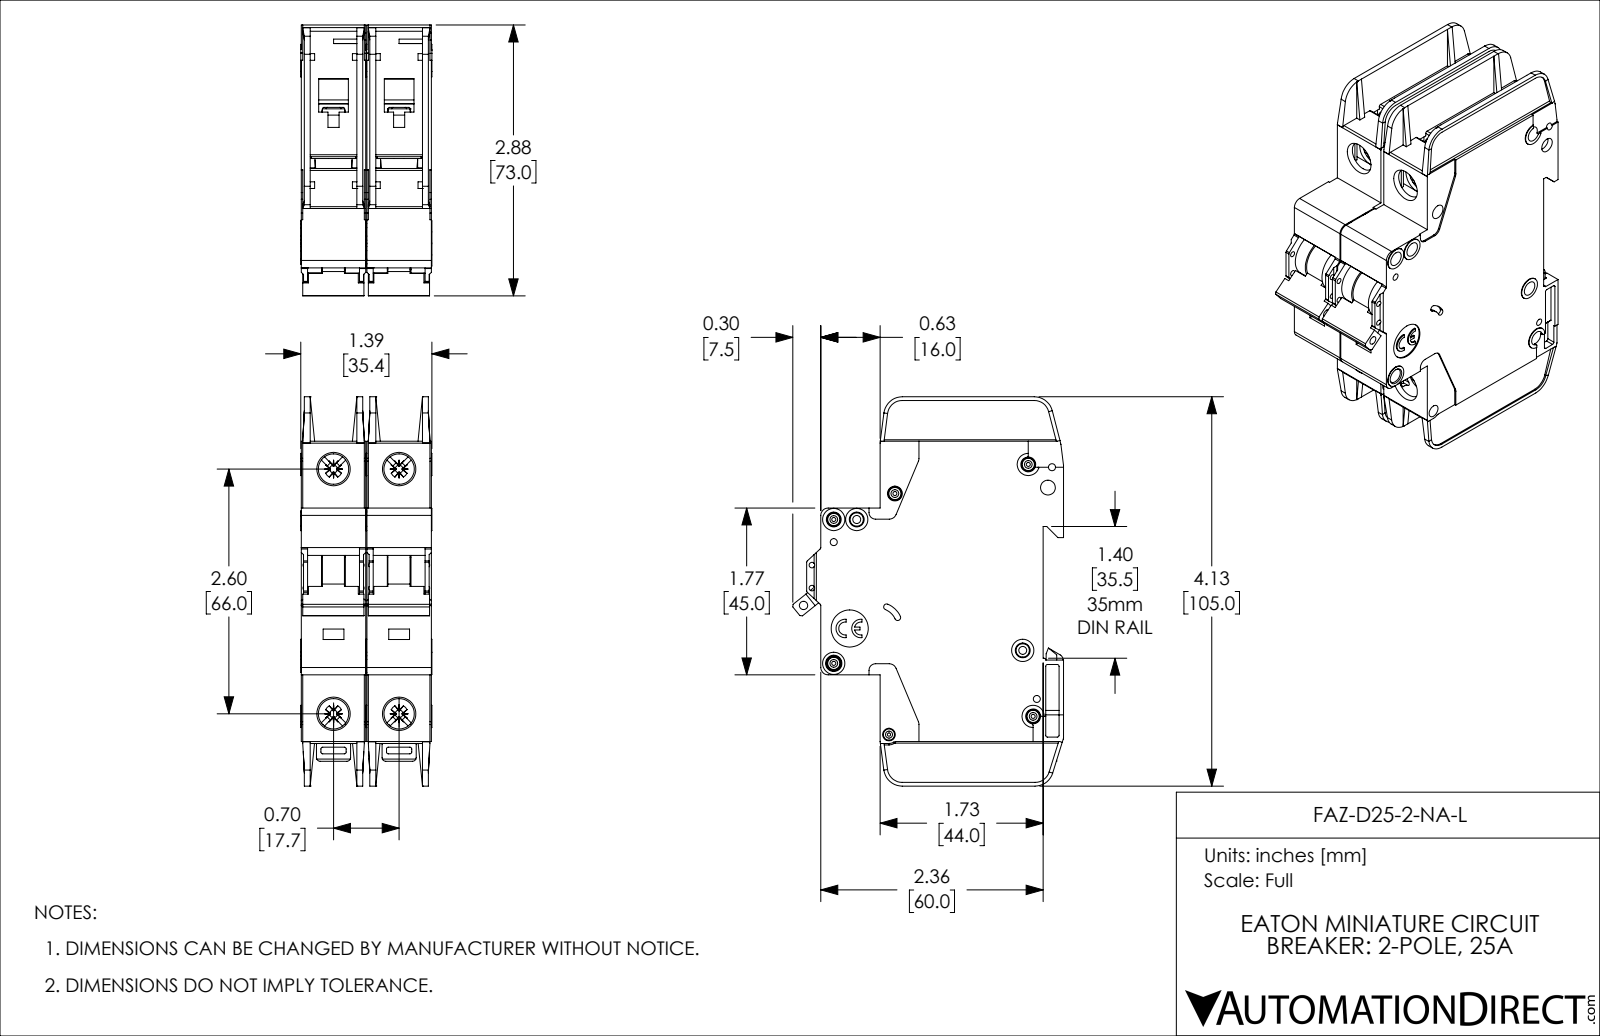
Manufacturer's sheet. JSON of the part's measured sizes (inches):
{"part_name": "FAZ-D25-2-NA-L", "step_written_by": "SolidWorks 2019 (AUTOMOTIVE_DESIGN)", "units": "inches", "bodies": {"solids": 2, "faces": 2254, "planar": 1342, "cylindrical": 714, "other": 198}, "overall_size": [4.134, 2.876, 1.394], "volume_in3": 9.365, "surface_area_in2": 82.01, "round_holes": [[0.157, 8], [0.043, 5], [0.075, 4], [0.323, 4], [0.059, 2], [0.085, 2], [0.035, 1], [0.089, 1], [0.098, 1], [0.134, 1], [0.394, 1]], "round_bosses_or_shafts": [[0.13, 5], [0.236, 4], [0.118, 3], [0.098, 2]], "partial_cylinders_radius": [[0.02, 57], [0.016, 20], [0.039, 14], [0.079, 10], [0.043, 8], [0.008, 5], [0.197, 5], [0.01, 4]], "face_to_face_distances": [0.697, 0.047, 0.685, 0.591, 0.094, 0.638, 0.543, 1.382, 0.744, 0.65], "hole_center_spacings": [0.244, 0.537, 0.697, 0.87, 2.598, 2.69, 0.189, 0.199]}
